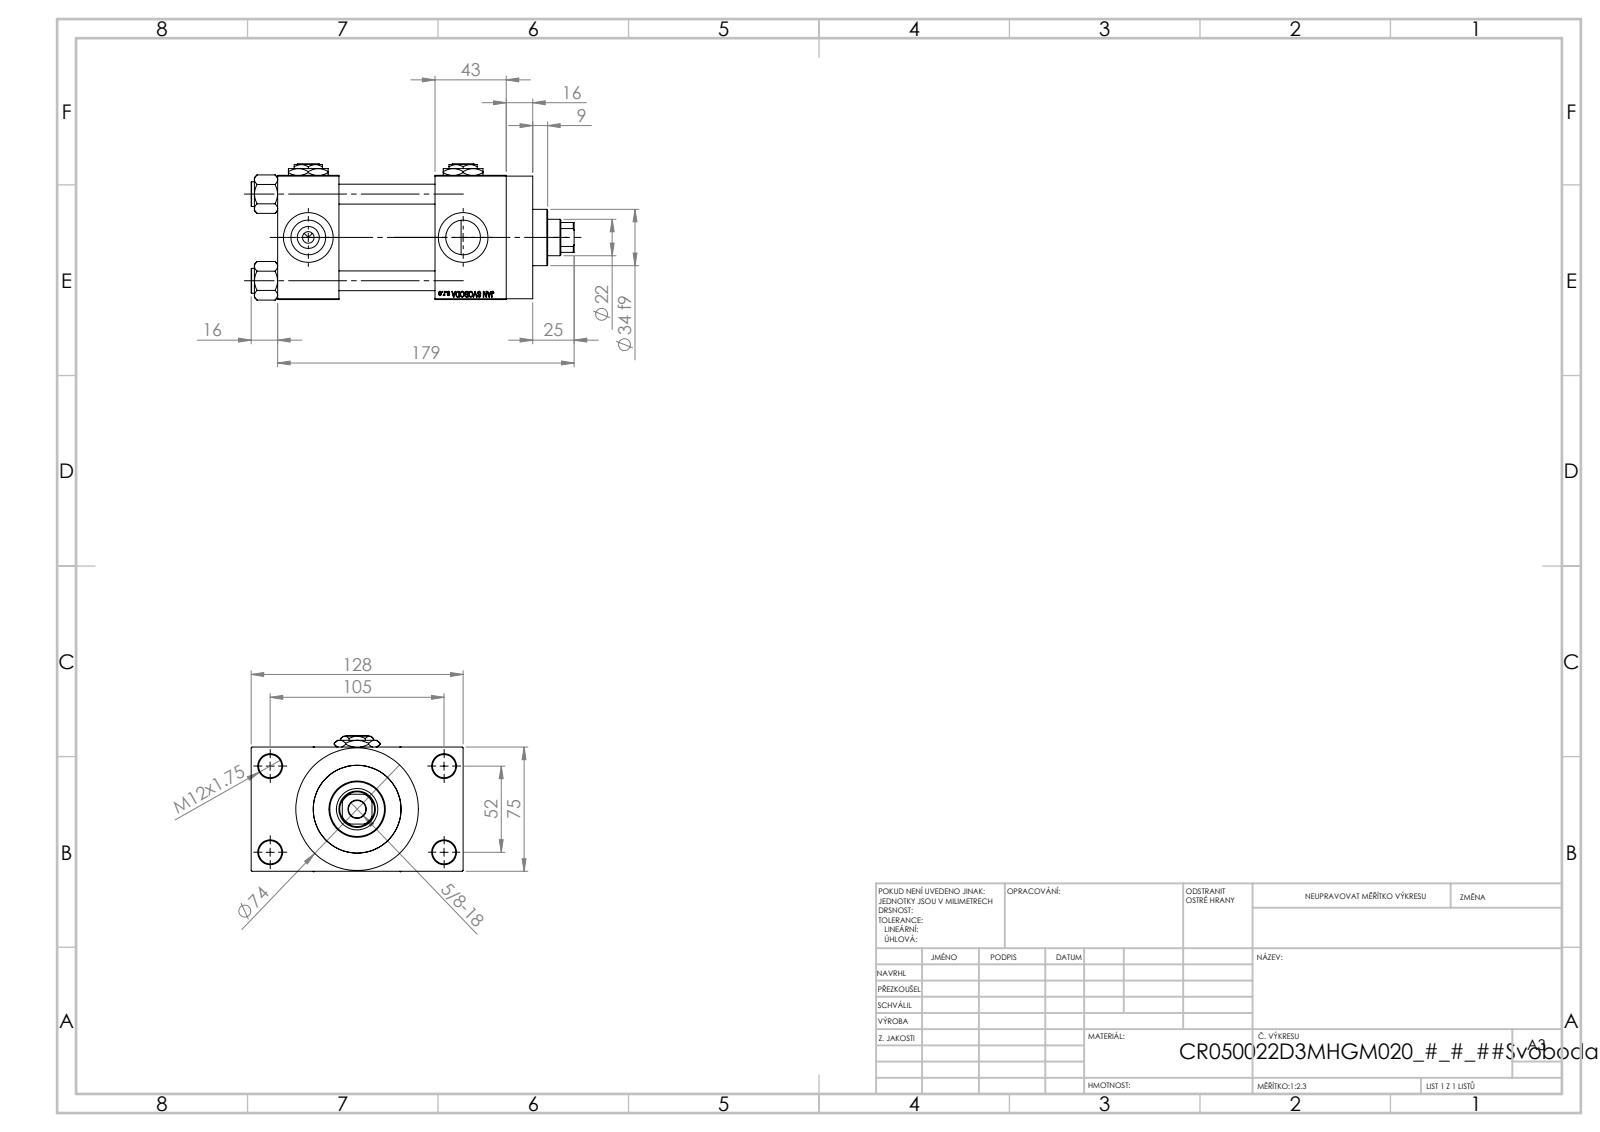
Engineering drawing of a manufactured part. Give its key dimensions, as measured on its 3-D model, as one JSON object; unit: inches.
{"part_name": "V215CR_D_Body; V215CR_D_TYCINKA; V215_VC_A; Zatka_pro_OIL_PORT (+2 more)", "step_written_by": "SolidWorks 2019 (CONFIG_CONTROL_DESIGN)", "units": "inches", "bodies": {"solids": 13, "faces": 1204, "planar": 545, "cylindrical": 99, "other": 560}, "overall_size": [7.677, 5.039, 3.239], "volume_in3": 48.4, "surface_area_in2": 264.9, "round_holes": [[0.472, 4], [0.551, 4], [0.825, 4], [1.181, 4], [0.276, 3], [0.413, 1], [0.866, 1], [0.984, 1], [1.614, 1], [1.969, 1], [2.087, 1]], "round_bosses_or_shafts": [[0.591, 4], [2.913, 1], [2.205, 1], [1.339, 1]], "partial_cylinders_radius": [[0.413, 1]], "face_to_face_distances": [2.953, 2.283, 1.457, 3.74, 1.043, 5.433, 3.976, 1.693, 3.996, 0.63], "hole_center_spacings": [1.037, 1.456, 2.059, 2.3, 2.307, 3.096, 3.715, 2.047]}
